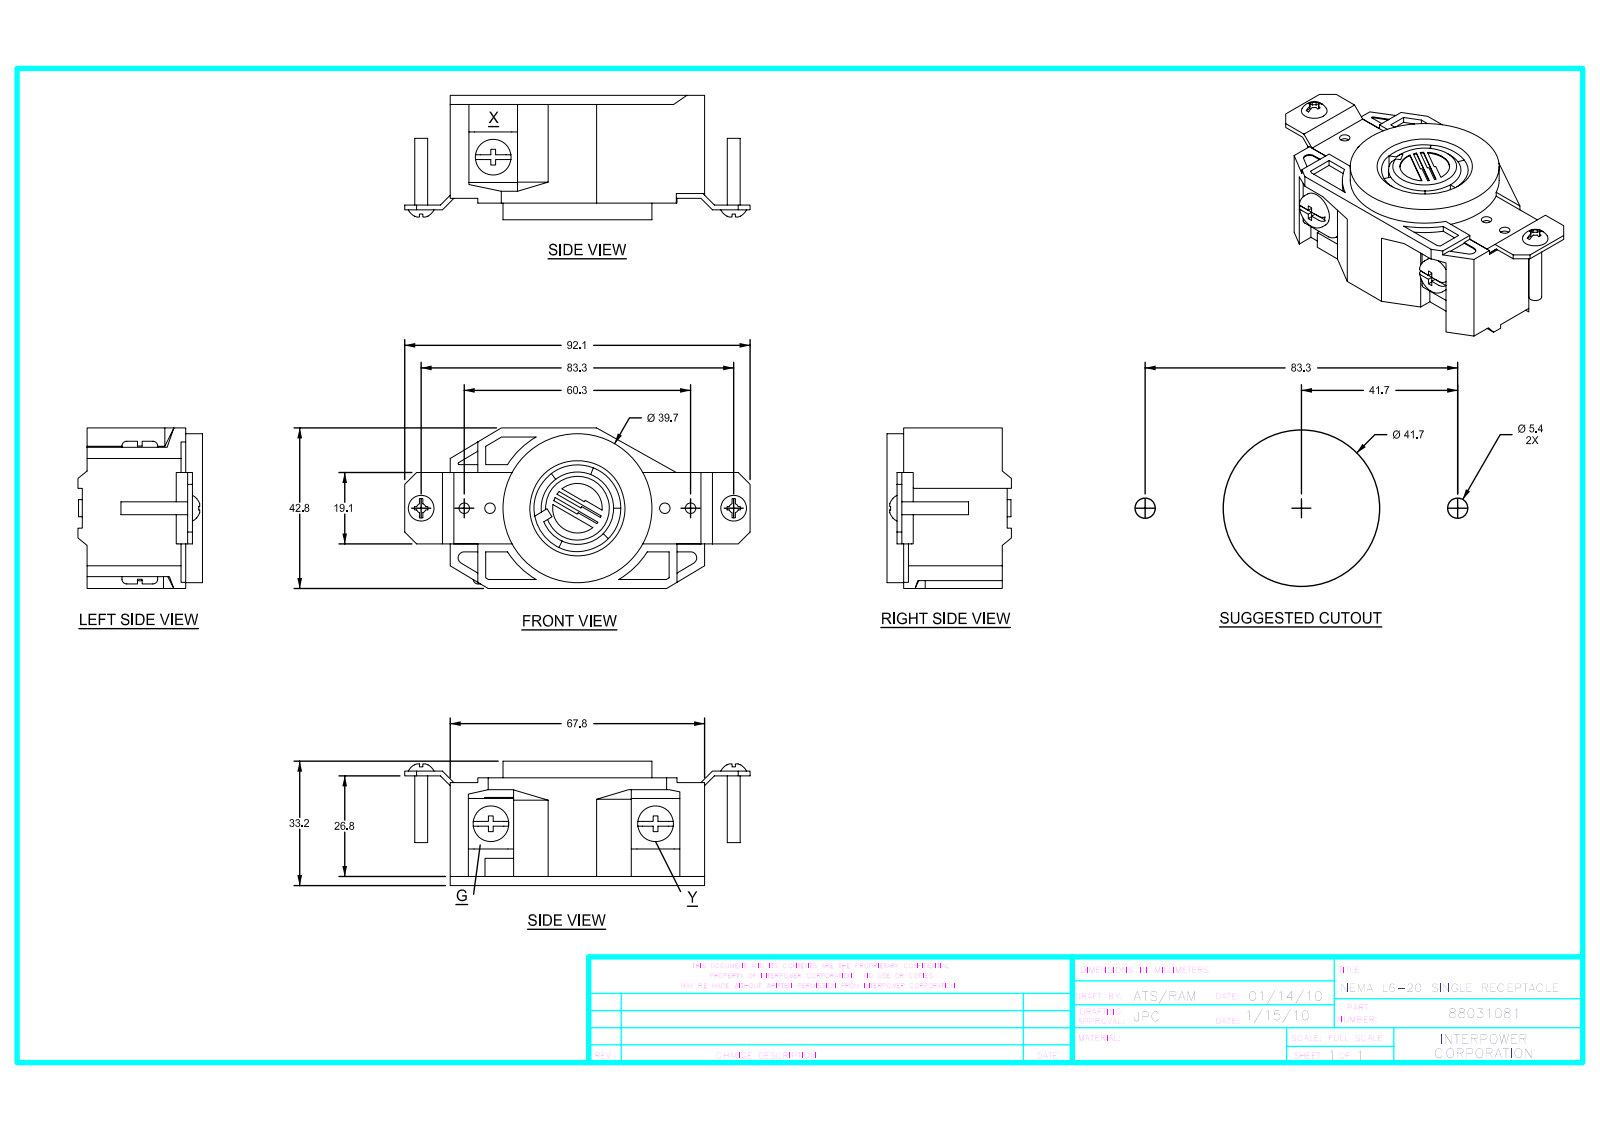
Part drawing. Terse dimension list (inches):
name: 88031081
written by: SolidWorks 2009 (CONFIG_CONTROL_DESIGN)
unit: in
bodies: 9 solids, 330 faces (248 planar, 67 cylindrical, 15 other)
size: 3.625 × 1.685 × 1.306
volume: 4.088 in³; area: 29.97 in²
holes: 4× ⌀0.11, 1× ⌀0.52, 1× ⌀1.563
bosses: 3× ⌀0.375, 2× ⌀0.18, 2× ⌀0.135
rounds: 6× R0.01, 6× R0.06, 2× R0.05, 2× R0.063, 1× R0.011, 1× R0.38, 1× R0.455, 1× R0.864
face distances: 0.05, 0.976, 1.026, 0.926, 0.1, 0.935, 1.21, 1.2, 0.275, 0.12
hole spacings: 0.27, 0.917, 1.187, 2.105, 1.835, 2.375
